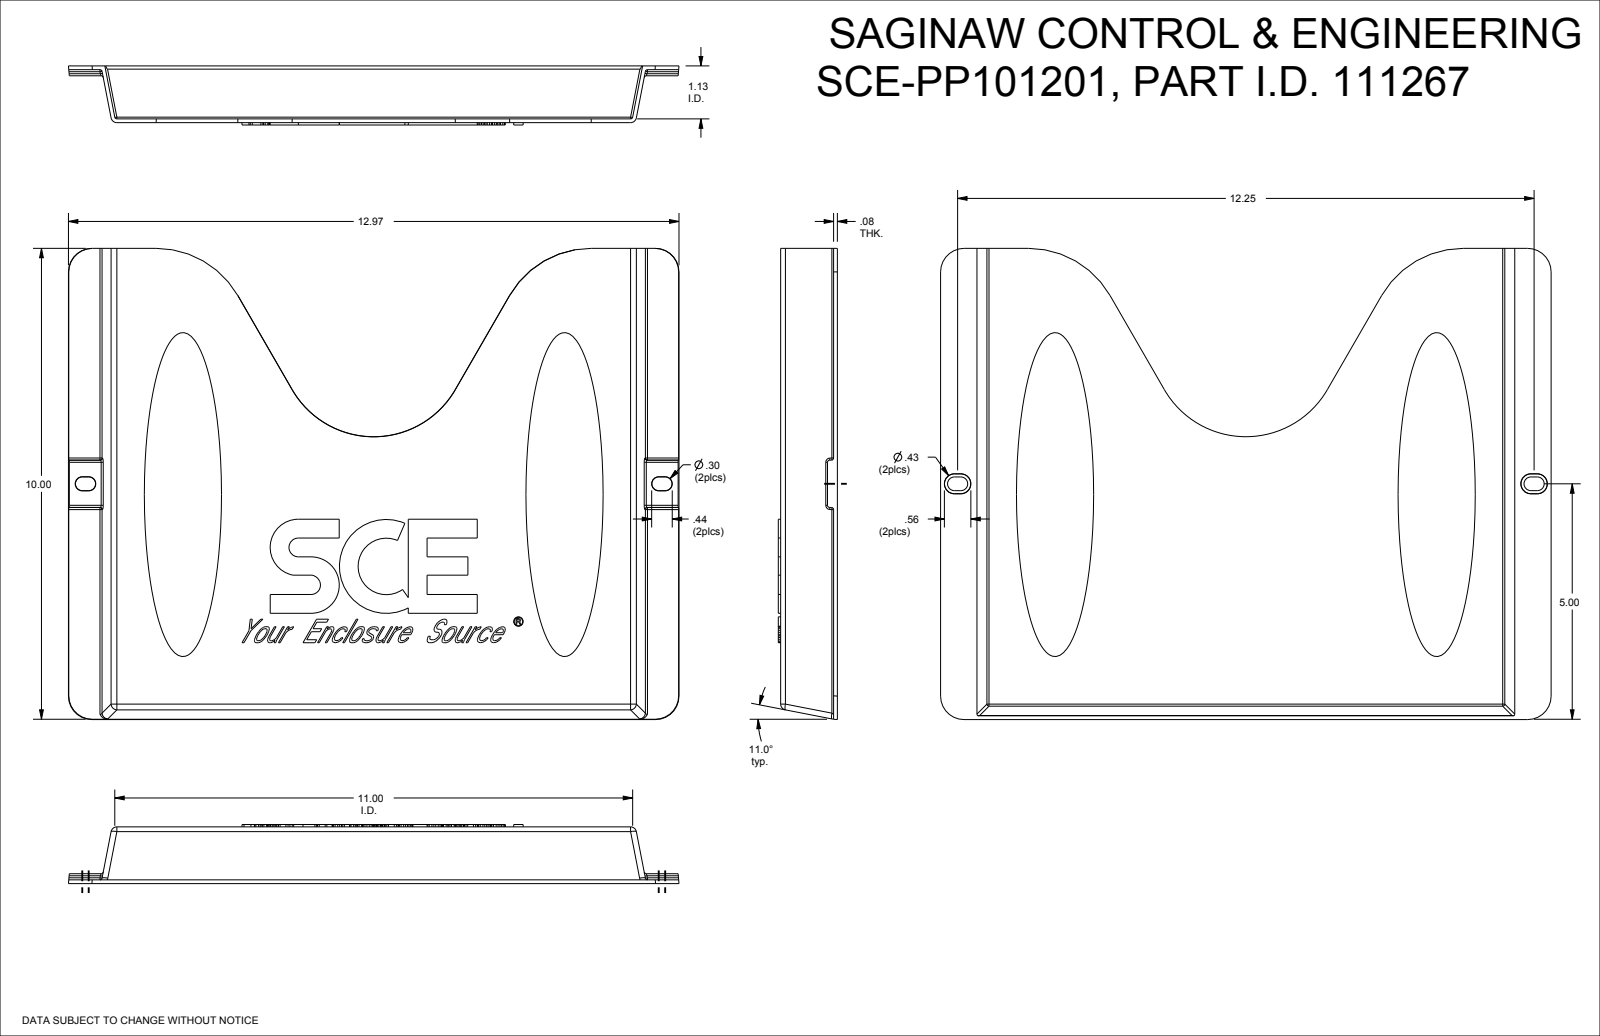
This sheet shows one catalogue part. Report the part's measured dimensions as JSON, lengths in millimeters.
{"part_name": "SCE-PP101201", "step_written_by": "SolidWorks 2021 (AUTOMOTIVE_DESIGN)", "units": "millimeters", "bodies": {"solids": 1, "faces": 774, "planar": 704, "cylindrical": 45, "other": 25}, "overall_size": [329.5, 254.2, 32.9], "volume_mm3": 165700, "surface_area_mm2": 162900, "round_holes": [[4.6, 1]], "round_bosses_or_shafts": [[5.1, 1]], "partial_cylinders_radius": [[1.1, 17], [3.2, 5], [12.7, 4], [15.2, 3], [5.1, 2], [50.8, 2], [5.7, 1], [25.3, 1]], "face_to_face_distances": [2, 28.6, 30.6, 26.5, 3.3, 1.3, 31.9, 29.8, 5.3, 23.2]}
